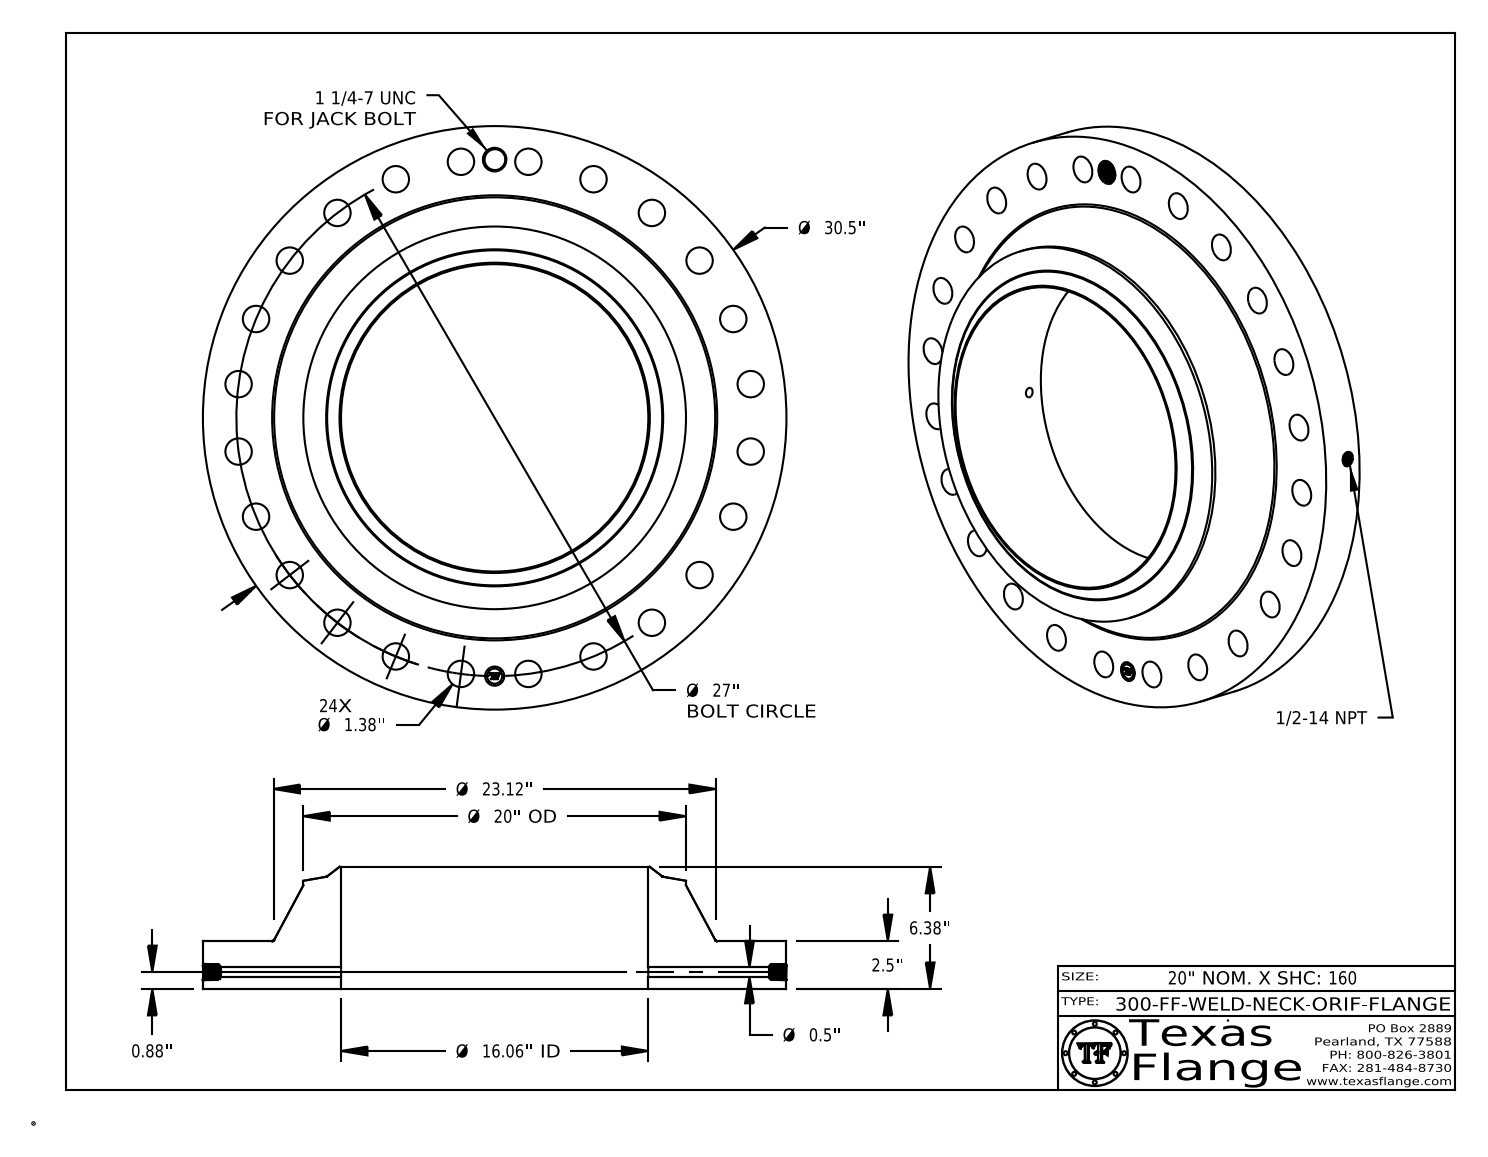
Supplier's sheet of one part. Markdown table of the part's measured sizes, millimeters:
| quantity | value |
| --- | --- |
| part name | 300-FF-WELD-NECK |
| STEP written by | CATIA V5 STEP AP214 (AUTOMOTIVE_DESIGN) |
| units | millimeters |
| bodies | 1 solid, 819 faces (368 planar, 129 cylindrical, 322 other) |
| overall size | 774.7 × 774.7 × 162.1 |
| volume | 28 730 000 mm³ |
| surface area | 1 281 000 mm² |
| round holes (diameter × count) | 35.1 × 24, 12.7 × 1, 17.1 × 1, 25.4 × 1, 28.2 × 1, 408 × 1 |
| round bosses / shafts (diameter × count) | 1.5 × 8, 774.7 × 1, 508 × 1, 20 × 1 |
| main face-to-face distances | 63.5, 162.1, 98.6, 63.1, 0.4, 98.9, 7.6, 7.4, 1.4, 6.3 |
| hole center spacings | 342.9, 593.9, 633.6, 544.1, 89.5, 177.5, 484.9, 662.4 |
